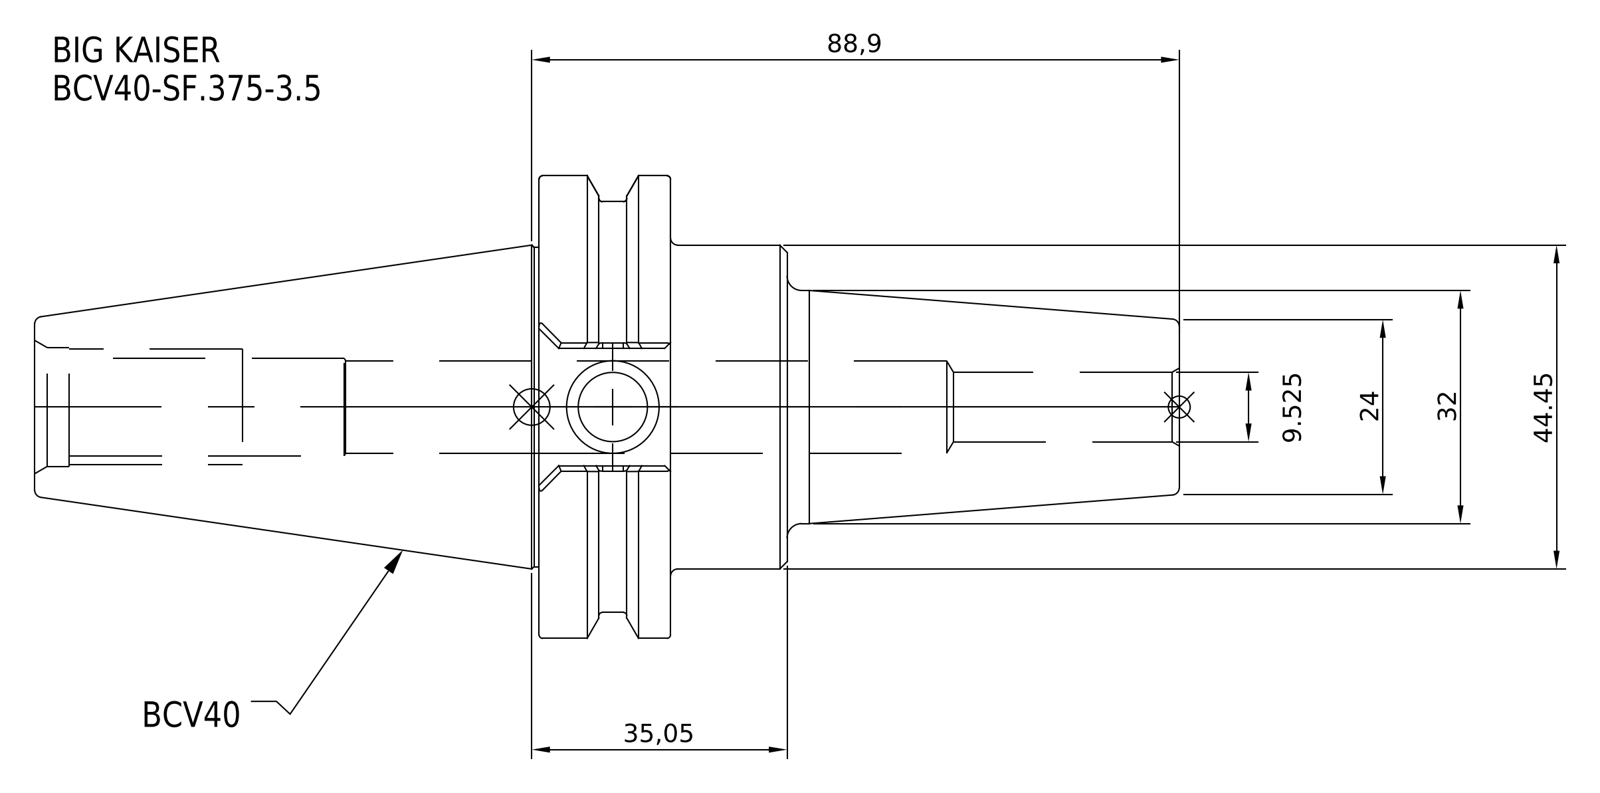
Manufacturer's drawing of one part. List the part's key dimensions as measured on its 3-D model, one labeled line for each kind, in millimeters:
Part name (STEP PRODUCT): BCV40-SF_375-3_5
STEP written by: SolidWorks 2021 (CONFIG_CONTROL_DESIGN)
Units: millimetres
Bodies: 1 solid, 30 faces (8 planar, 14 cylindrical, 8 other)
Overall size (bounding box): 157.15 × 63.5 × 63.5
Volume: 177 389 mm³ · Surface area: 24 852 mm²
Round holes (diameter × count): ⌀9.52 ×1
Round bosses / shafts (diameter × count): ⌀63.5 ×1, ⌀56.36 ×1, ⌀44.45 ×1, ⌀32 ×1
Main face-to-face distances: 18.05, 16, 34.05, 103.3, 87.3, 69.25, 53.85, 69.85, 87.9, 157.15
